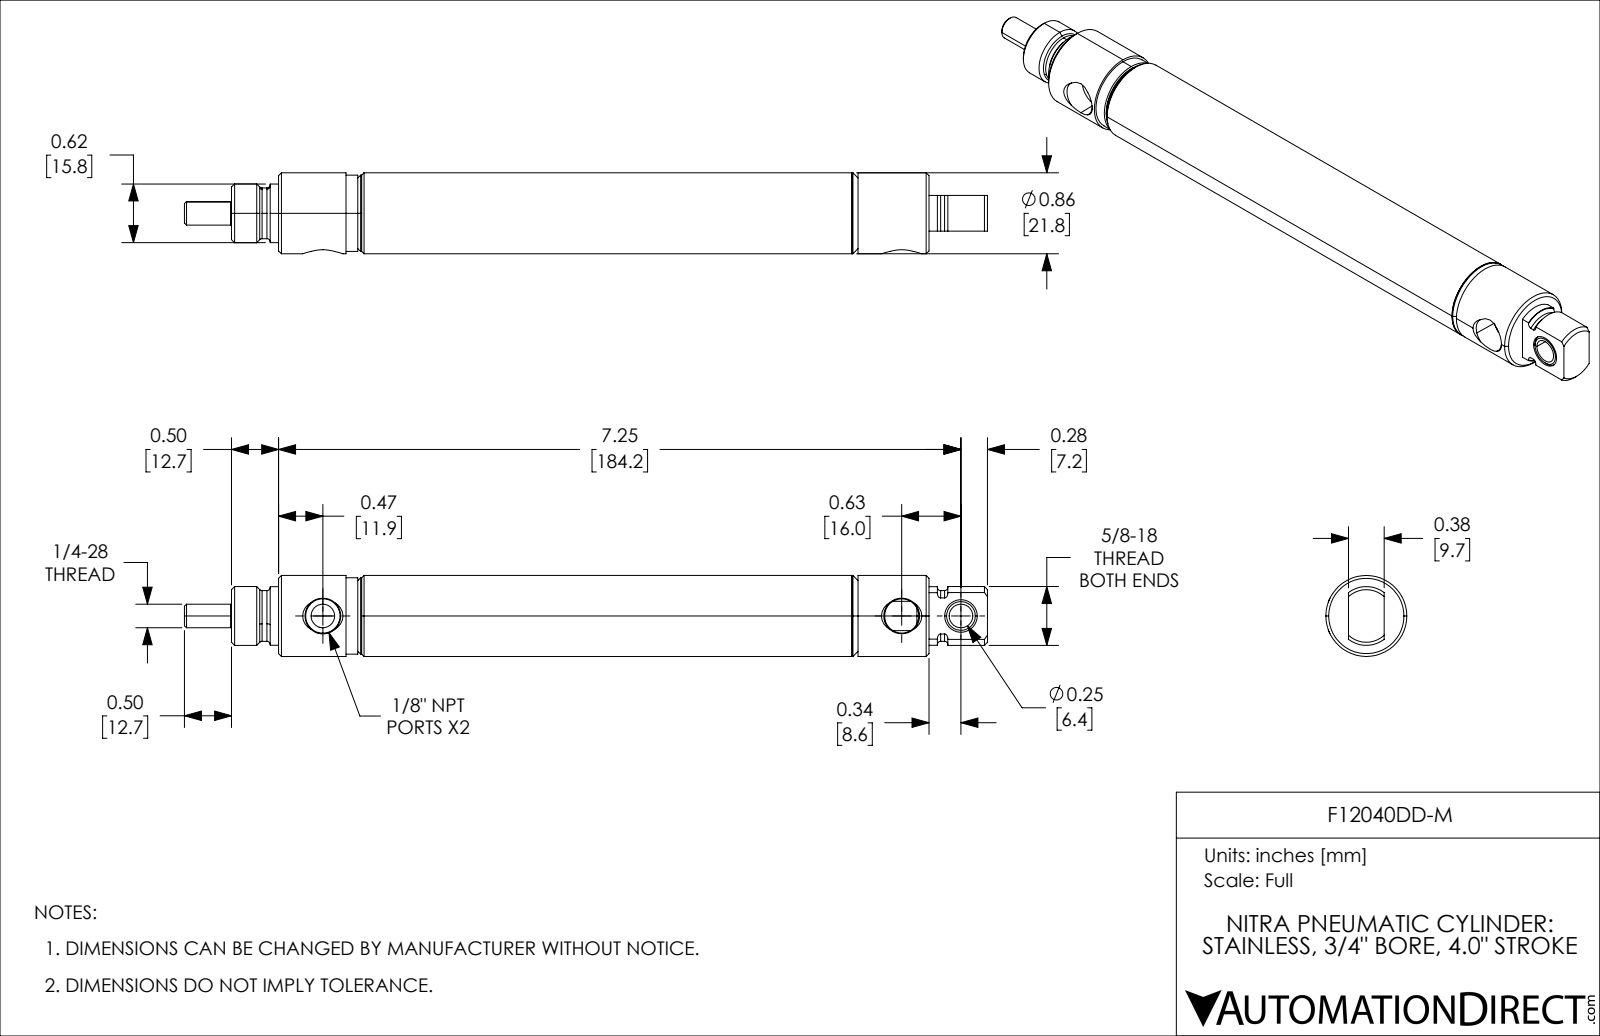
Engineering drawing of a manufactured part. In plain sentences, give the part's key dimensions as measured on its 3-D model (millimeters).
The part is named "F12040DD-M_7; F12040DD-M; F12040DD-M_9; F12040DD-M_3 (+2 more)". Its 3-D file was written by "SolidWorks 2021 (CONFIG_CONTROL_DESIGN)". It is 5 solids with 158 faces: 29 planar, 61 cylindrical and 68 other. Overall it measures 216.71 by 21.84 by 21.84 millimeters. Its volume is 40 686 cubic millimeters and its surface area 31 613 square millimeters. Round holes: 1 of diameter 6.35, 1 of diameter 6.38, 1 of diameter 6.95, 1 of diameter 7.92, 1 of diameter 8.78, 1 of diameter 9.23, 1 of diameter 12.7, 1 of diameter 17.83. Round bosses or shafts: 1 of diameter 21.84, 1 of diameter 20.57, 1 of diameter 19.35, 1 of diameter 15.88, 1 of diameter 15.81, 1 of diameter 13.68, 1 of diameter 6.35, 1 of diameter 5.84. Partial cylindrical surfaces (rounded edges, fillets, slot ends): 1 of radius 6.84. The main face-to-face distances are 21.43, 40.49, 163.52, 101.6, 123.03, 147.72, 46.12, 24.69, 12.7, 9.66. The hole center spacings are 16, 156.21, 172.21.
